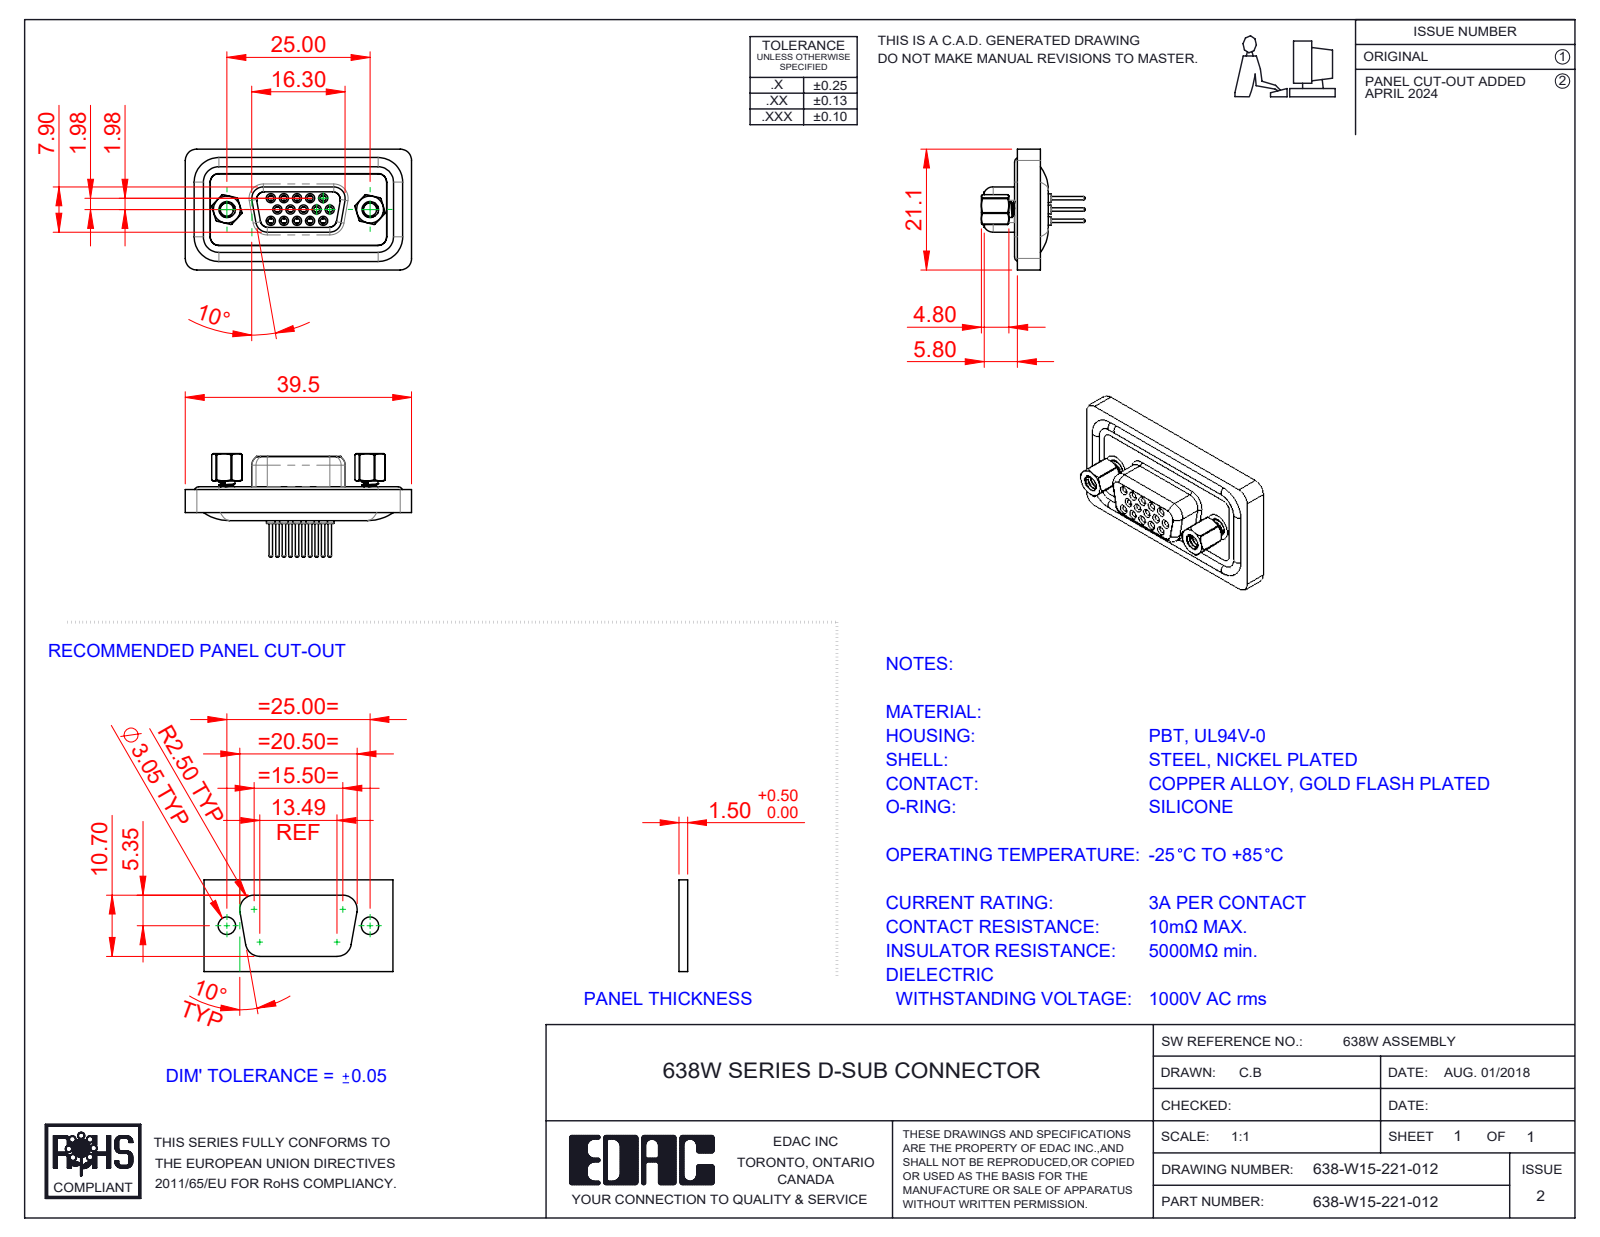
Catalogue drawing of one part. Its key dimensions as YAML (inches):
part_name: "638-W15-221-012; 638W Contact Row 1_21; 638W Contact Row 3_21; 638W Shell_15 Contacts (+5 more)"
step_written_by: "SolidWorks 2016 (CONFIG_CONTROL_DESIGN)"
units: inches
bodies: {solids: 23, faces: 1276, planar: 326, cylindrical: 531, other: 419}
overall_size: [1.556, 0.831, 0.695]
volume: 0.264
surface_area: 12.56
round_holes:
  - {diameter: 0.039, count: 15}
  - {diameter: 0.043, count: 15}
  - {diameter: 0.059, count: 15}
  - {diameter: 0.067, count: 15}
  - {diameter: 0.071, count: 15}
  - {diameter: 0.079, count: 15}
  - {diameter: 0.089, count: 2}
  - {diameter: 0.09, count: 2}
  - {diameter: 0.157, count: 2}
  - {diameter: 0.189, count: 2}
  - {diameter: 0.197, count: 2}
round_bosses_or_shafts:
  - {diameter: 0.063, count: 19}
  - {diameter: 0.087, count: 15}
  - {diameter: 0.024, count: 15}
  - {diameter: 0.059, count: 6}
  - {diameter: 0.193, count: 2}
  - {diameter: 0.11, count: 2}
  - {diameter: 0.197, count: 1}
partial_cylinders:
  - {radius: 0.059, count: 14}
  - {radius: 0.079, count: 14}
  - {radius: 0.053, count: 8}
  - {radius: 0.106, count: 6}
  - {radius: 0.02, count: 4}
  - {radius: 0.035, count: 4}
  - {radius: 0.063, count: 4}
  - {radius: 0.069, count: 4}
face_to_face_distances: [0.016, 0.114, 0.063, 0.043, 0.098, 0.071, 0.02, 0.142, 0.028, 0.157]
hole_center_spacings: [0.09, 0.156, 0.09, 0.18, 0.238, 0.238, 0.156, 0.324]
